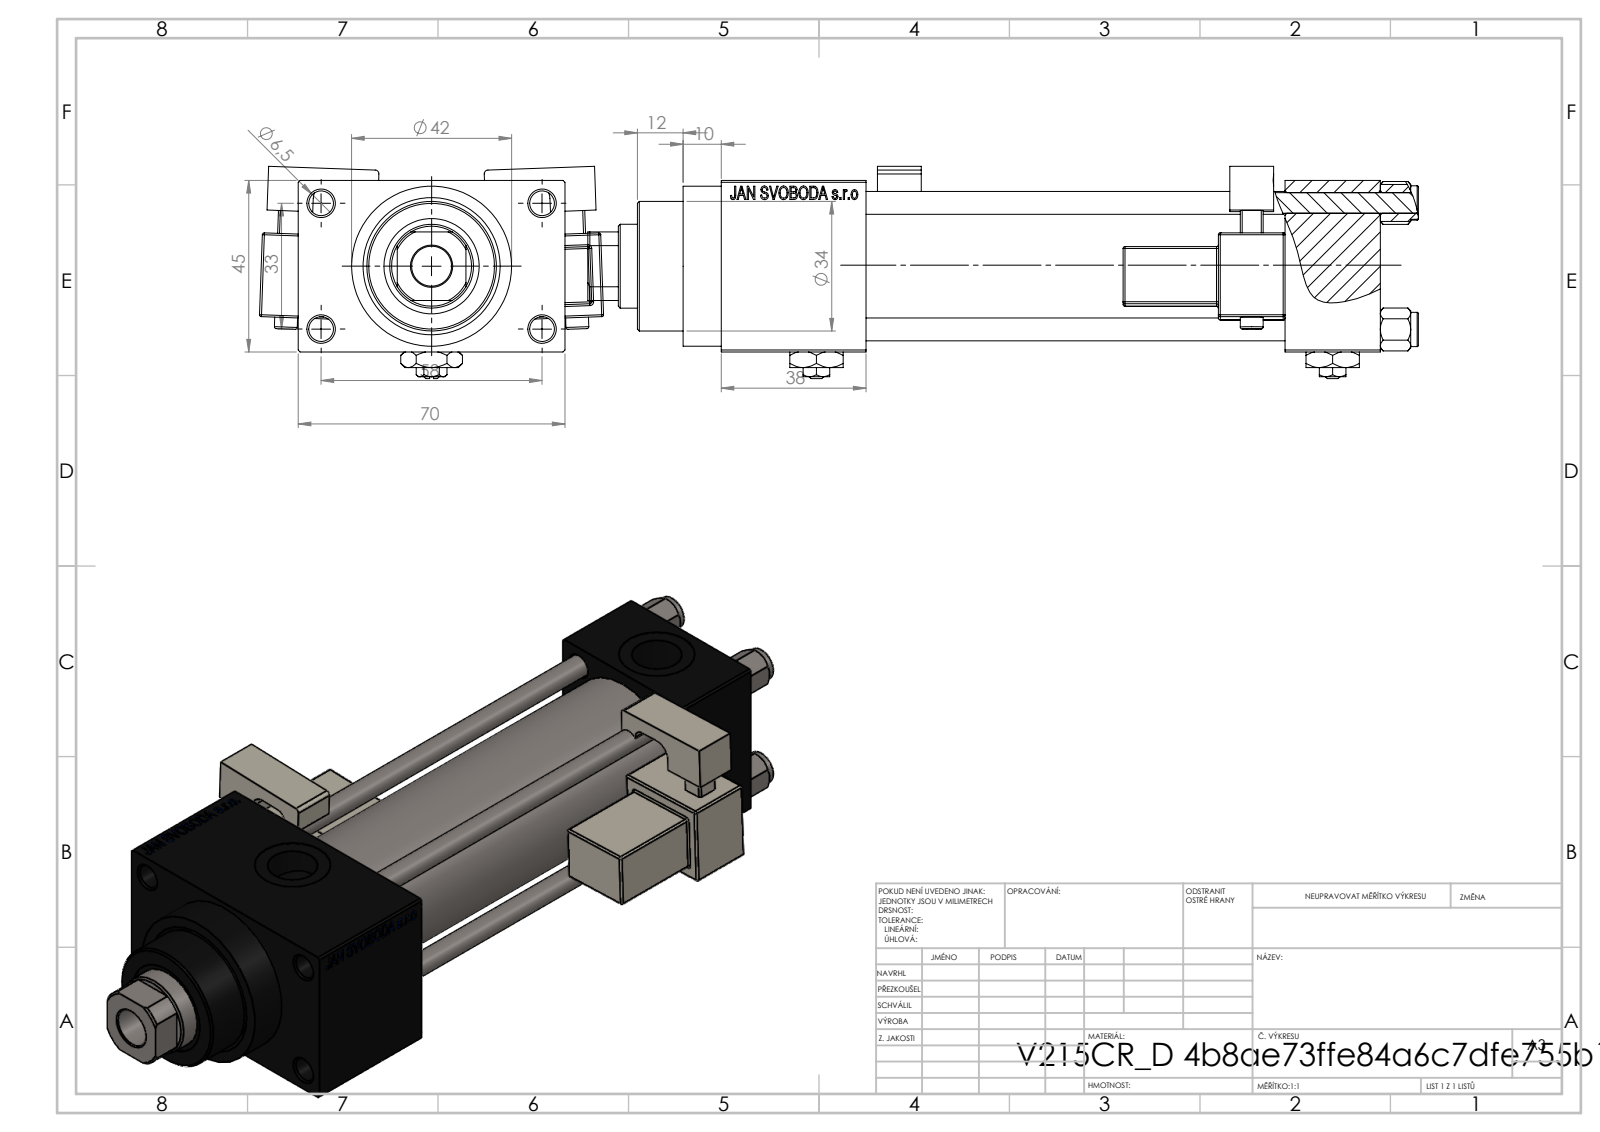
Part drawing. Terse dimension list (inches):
name: Zatka_pro_OIL_PORT; NUT_M5_D; V215_VC_A; V215CR_MSU (+3 more)
written by: SolidWorks 2019 (CONFIG_CONTROL_DESIGN)
unit: in
bodies: 15 solids, 1362 faces (604 planar, 160 cylindrical, 598 other)
size: 8.583 × 3.556 × 2.194
volume: 20.34 in³; area: 178.2 in²
holes: 4× ⌀0.236, 4× ⌀0.256, 2× ⌀0.276, 2× ⌀0.518, 2× ⌀0.787, 1× ⌀0.413, 1× ⌀0.866, 1× ⌀0.945, 1× ⌀0.984, 1× ⌀1.26, 1× ⌀1.299
bosses: 4× ⌀0.354, 2× ⌀0.236, 1× ⌀1.654, 1× ⌀1.496, 1× ⌀1.339
rounds: 48× R0.02, 2× R0.039, 2× R0.098, 2× R0.157, 1× R0.413
face distances: 1.772, 0.984, 0.492, 4.331, 0.118, 2.264, 5.315, 1.496, 5.827, 2.756
hole spacings: 0.488, 0.924, 1.307, 1.314, 1.392, 1.795, 2.219, 1.299
